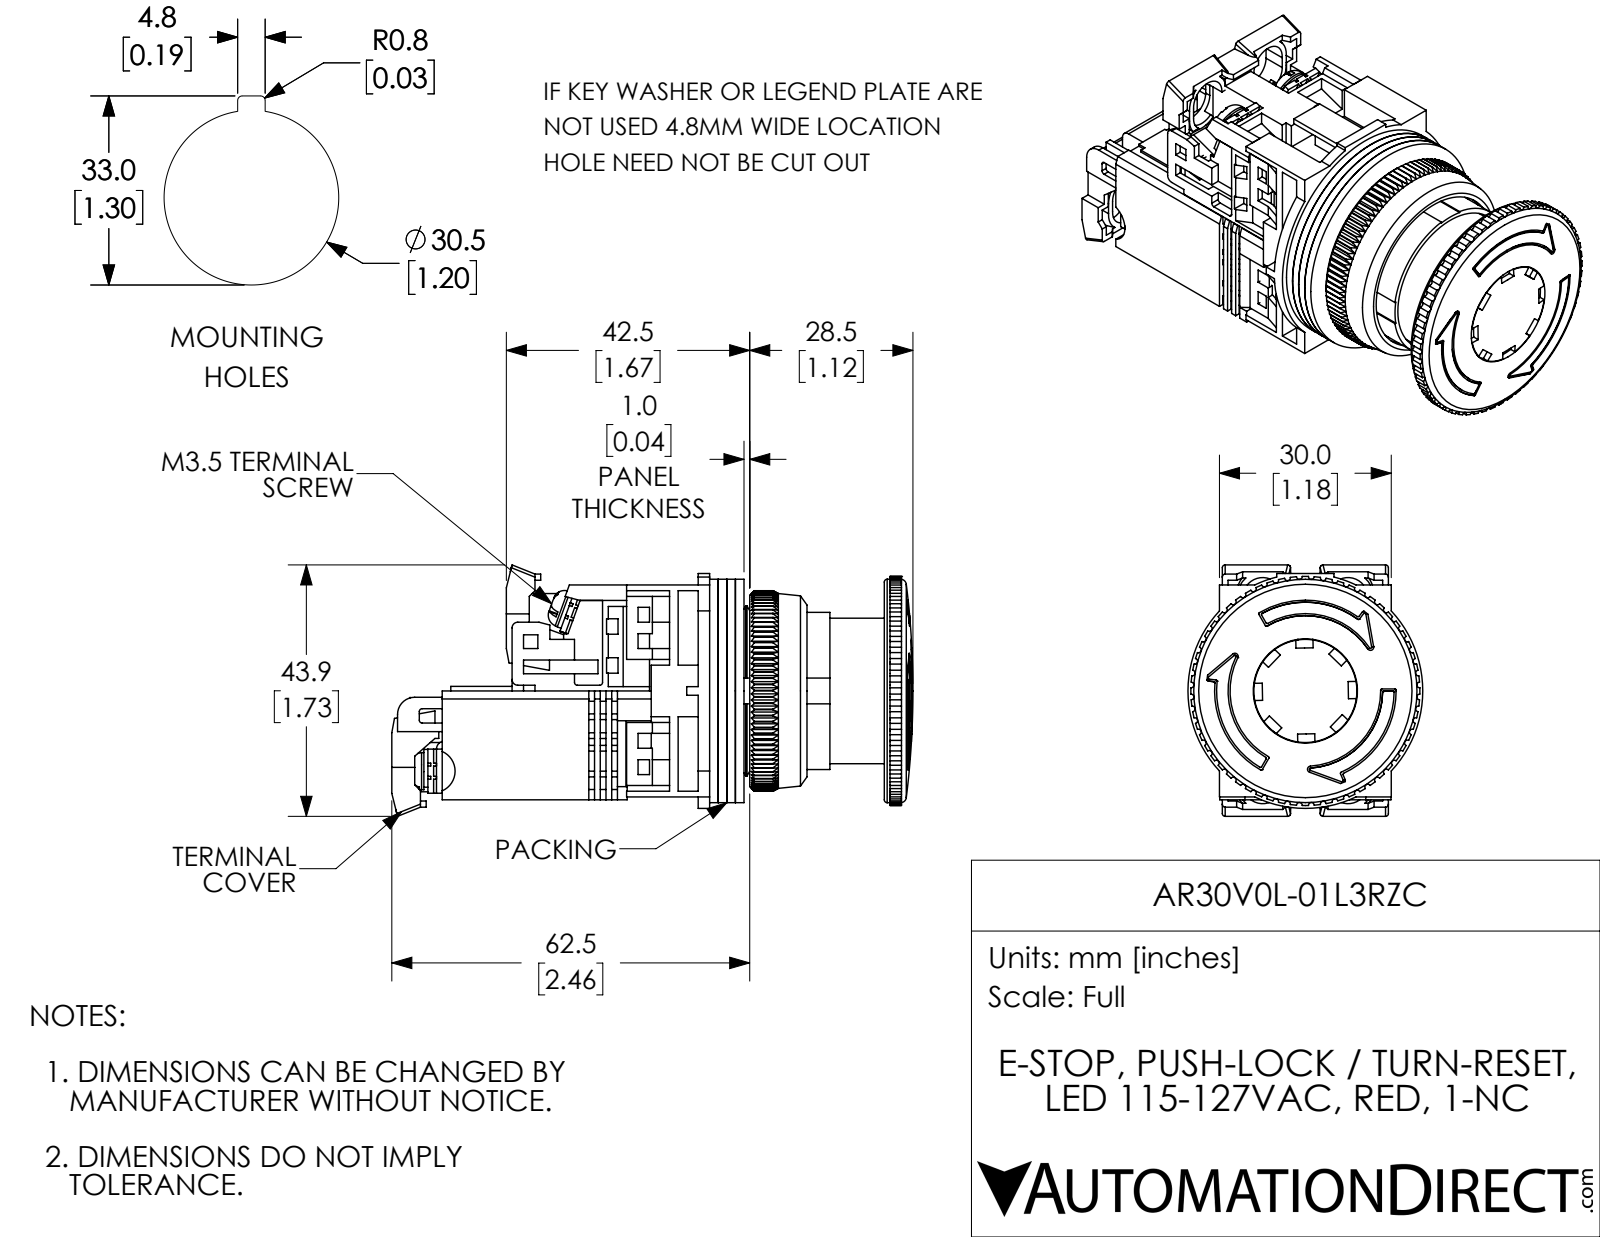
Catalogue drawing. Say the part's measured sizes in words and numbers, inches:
The part is named "AR30V0L-01L3RZC". Its 3-D file was written by "SolidWorks 2017 (AUTOMOTIVE_DESIGN)". It is 28 solids with 2341 faces: 1515 planar, 565 cylindrical and 261 other. Overall it measures 3.583 by 1.728 by 1.614 inches. Its volume is 3.556 cubic inches and its surface area 79.02 square inches. Round holes: 4 of diameter 0.138, 4 of diameter 0.142, 3 of diameter 0.118, 1 of diameter 0.217, 1 of diameter 0.335, 1 of diameter 0.453, 1 of diameter 0.543, 1 of diameter 0.571, 1 of diameter 0.63, 1 of diameter 0.709, 1 of diameter 0.717, 1 of diameter 0.803. Round bosses or shafts: 4 of diameter 0.26, 2 of diameter 0.138, 1 of diameter 1.535, 1 of diameter 1.181, 1 of diameter 1, 1 of diameter 0.787, 1 of diameter 0.531, 1 of diameter 0.413. Partial cylindrical surfaces (rounded edges, fillets, slot ends): 73 of radius 0.02, 24 of radius 0.008, 17 of radius 0.059, 6 of radius 0.022, 4 of radius 0.138, 4 of radius 0.177, 2 of radius 0.039, 2 of radius 0.118. The main face-to-face distances are 0.059, 0.118, 0.039, 0.748, 0.177, 0.787, 0.079, 0.728, 1.417, 0.138. The hole center spacings are 0.297, 0.624, 0.02, 0.302, 0.579, 0.583, 0.583, 0.606.
